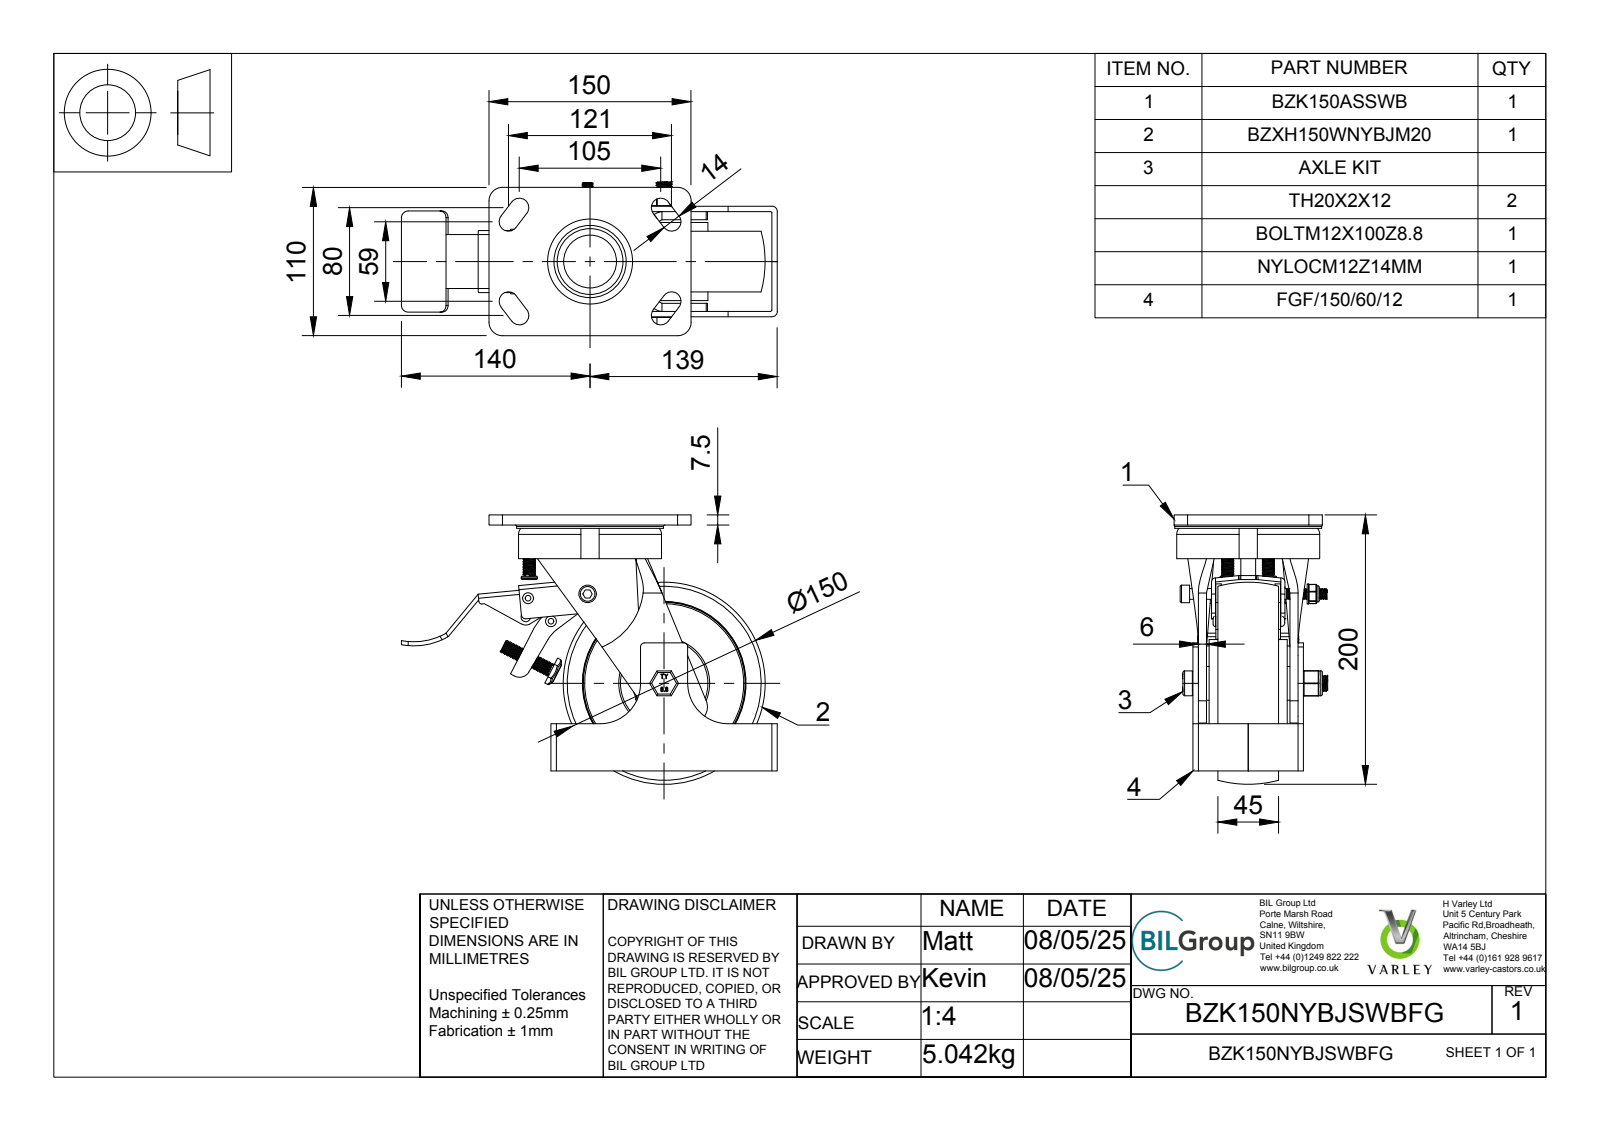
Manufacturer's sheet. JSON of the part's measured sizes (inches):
{"part_name": "BZK150NYBJSWBFG v3; BZXH150WNYBJM20 v1; BEARING6204; BEARING62042 (+7 more)", "step_written_by": "Autodesk Translation Framework v14.4.0.0 (AUTOMOTIVE_DESIGN)", "units": "inches", "bodies": {"solids": 52, "faces": 1494, "planar": 566, "cylindrical": 435, "other": 493}, "overall_size": [10.984, 7.874, 4.488], "volume_in3": 64.26, "surface_area_in2": 524.2, "round_holes": [[0.236, 5], [0.551, 2], [0.315, 1], [0.394, 1], [0.472, 1], [0.48, 1], [0.512, 1], [0.787, 1], [0.846, 1], [1.122, 1], [1.213, 1], [1.587, 1]], "round_bosses_or_shafts": [[0.472, 3], [0.315, 2], [0.236, 2], [4.291, 1], [4.213, 1], [2.559, 1], [1.606, 1], [1.232, 1]], "partial_cylinders_radius": [[0.02, 42], [0.039, 10], [0.118, 9], [0.276, 8], [0.049, 6], [0.157, 4], [0.197, 4], [0.394, 4]], "face_to_face_distances": [0.157, 1.378, 0.984, 3.071, 1.85, 1.22, 1.693, 2.913, 0.472, 0.295], "hole_center_spacings": [1.87, 0.554, 0.749, 0.952, 1.181, 1.336, 1.747, 1.931]}
